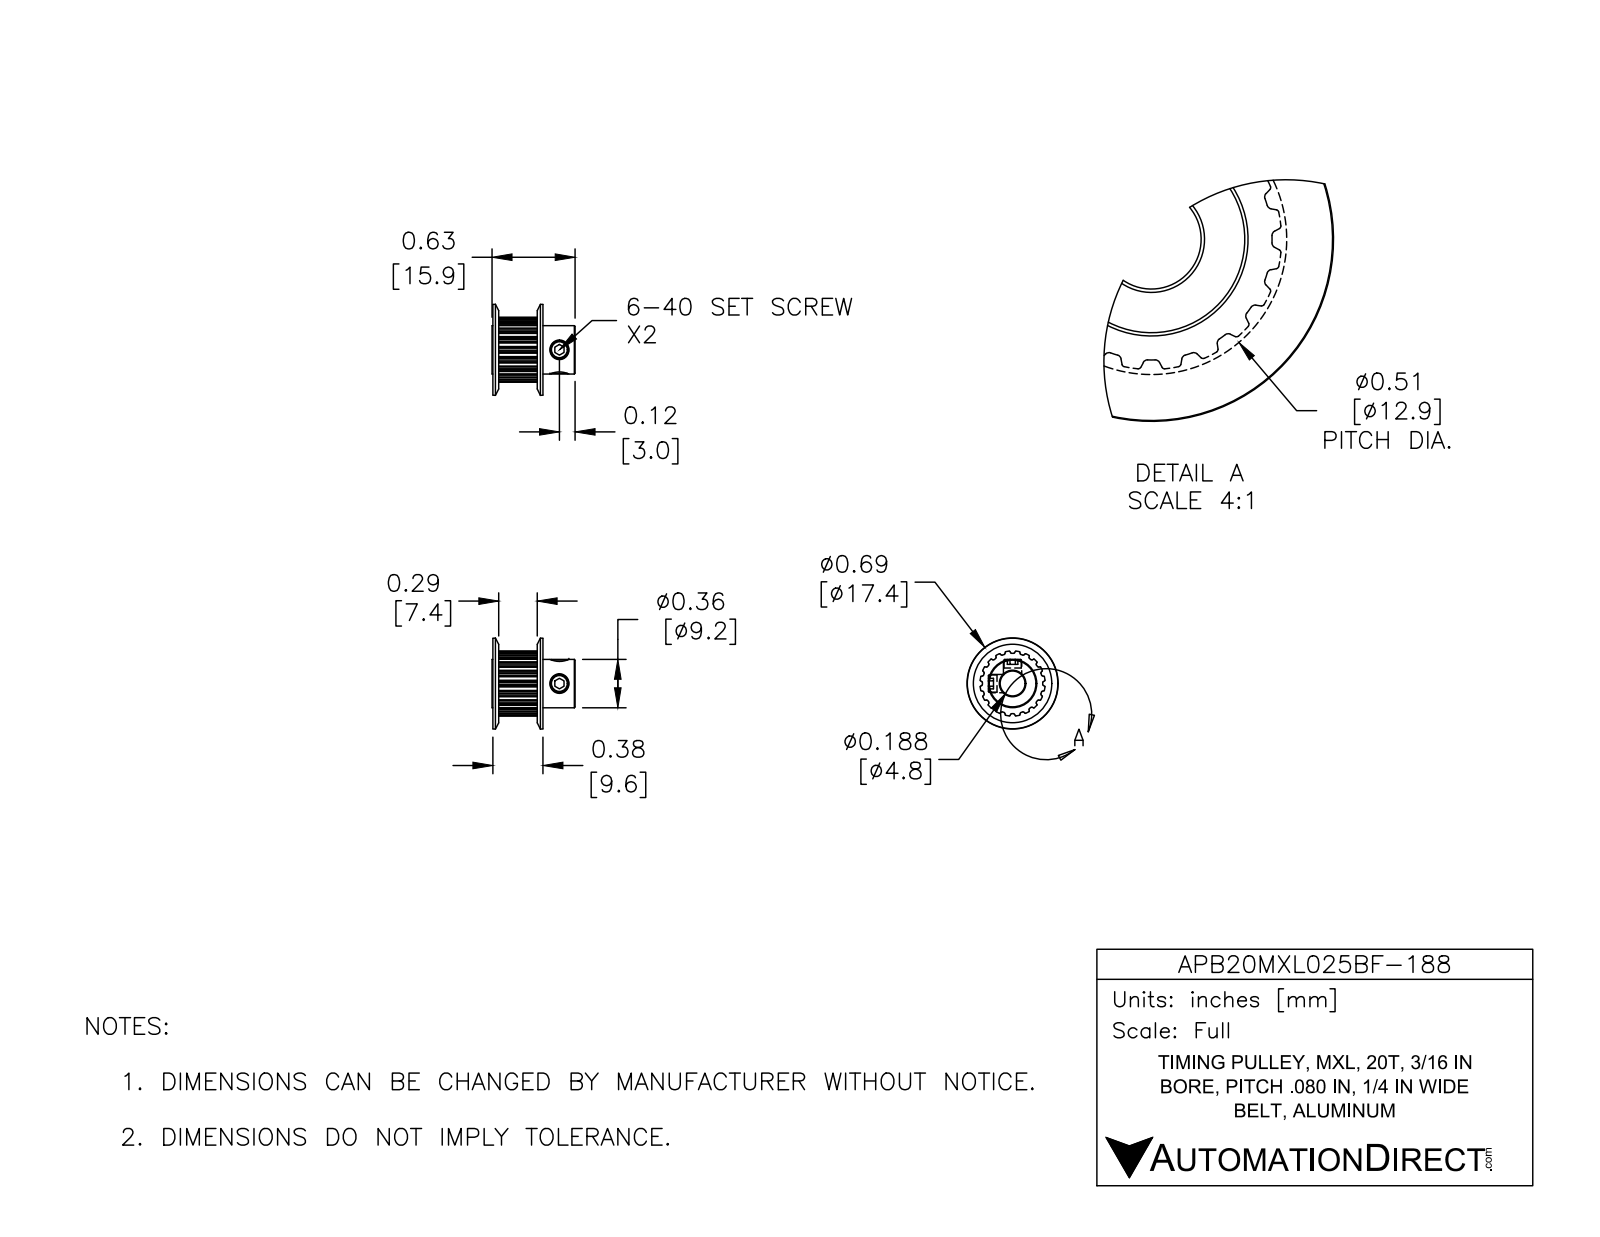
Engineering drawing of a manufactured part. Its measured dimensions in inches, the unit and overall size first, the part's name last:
Units: inches
Overall size (bounding box): 0.685 × 0.685 × 0.625
Round holes (diameter × count): ⌀0.138 ×2, ⌀0.187 ×1
Round bosses / shafts (diameter × count): ⌀0.13 ×2, ⌀0.364 ×1
Partial cylindrical surfaces — rounded edges, fillets, slot ends (radius × count): R0.005 ×40, R0.009 ×40, R0.227 ×1, R0.245 ×1
Main face-to-face distances: 0.339, 0.025, 0.364, 0.625, 0.6, 0.261, 0.191, 0.34, 0.315, 0.024
Volume: 0.079 in³ · Surface area: 2.531 in²
Bodies: 3 solids, 241 faces (64 planar, 151 cylindrical, 26 other)
Part name (STEP PRODUCT): APB20MXL025BF-188
STEP written by: SolidWorks 2016 (AUTOMOTIVE_DESIGN)
